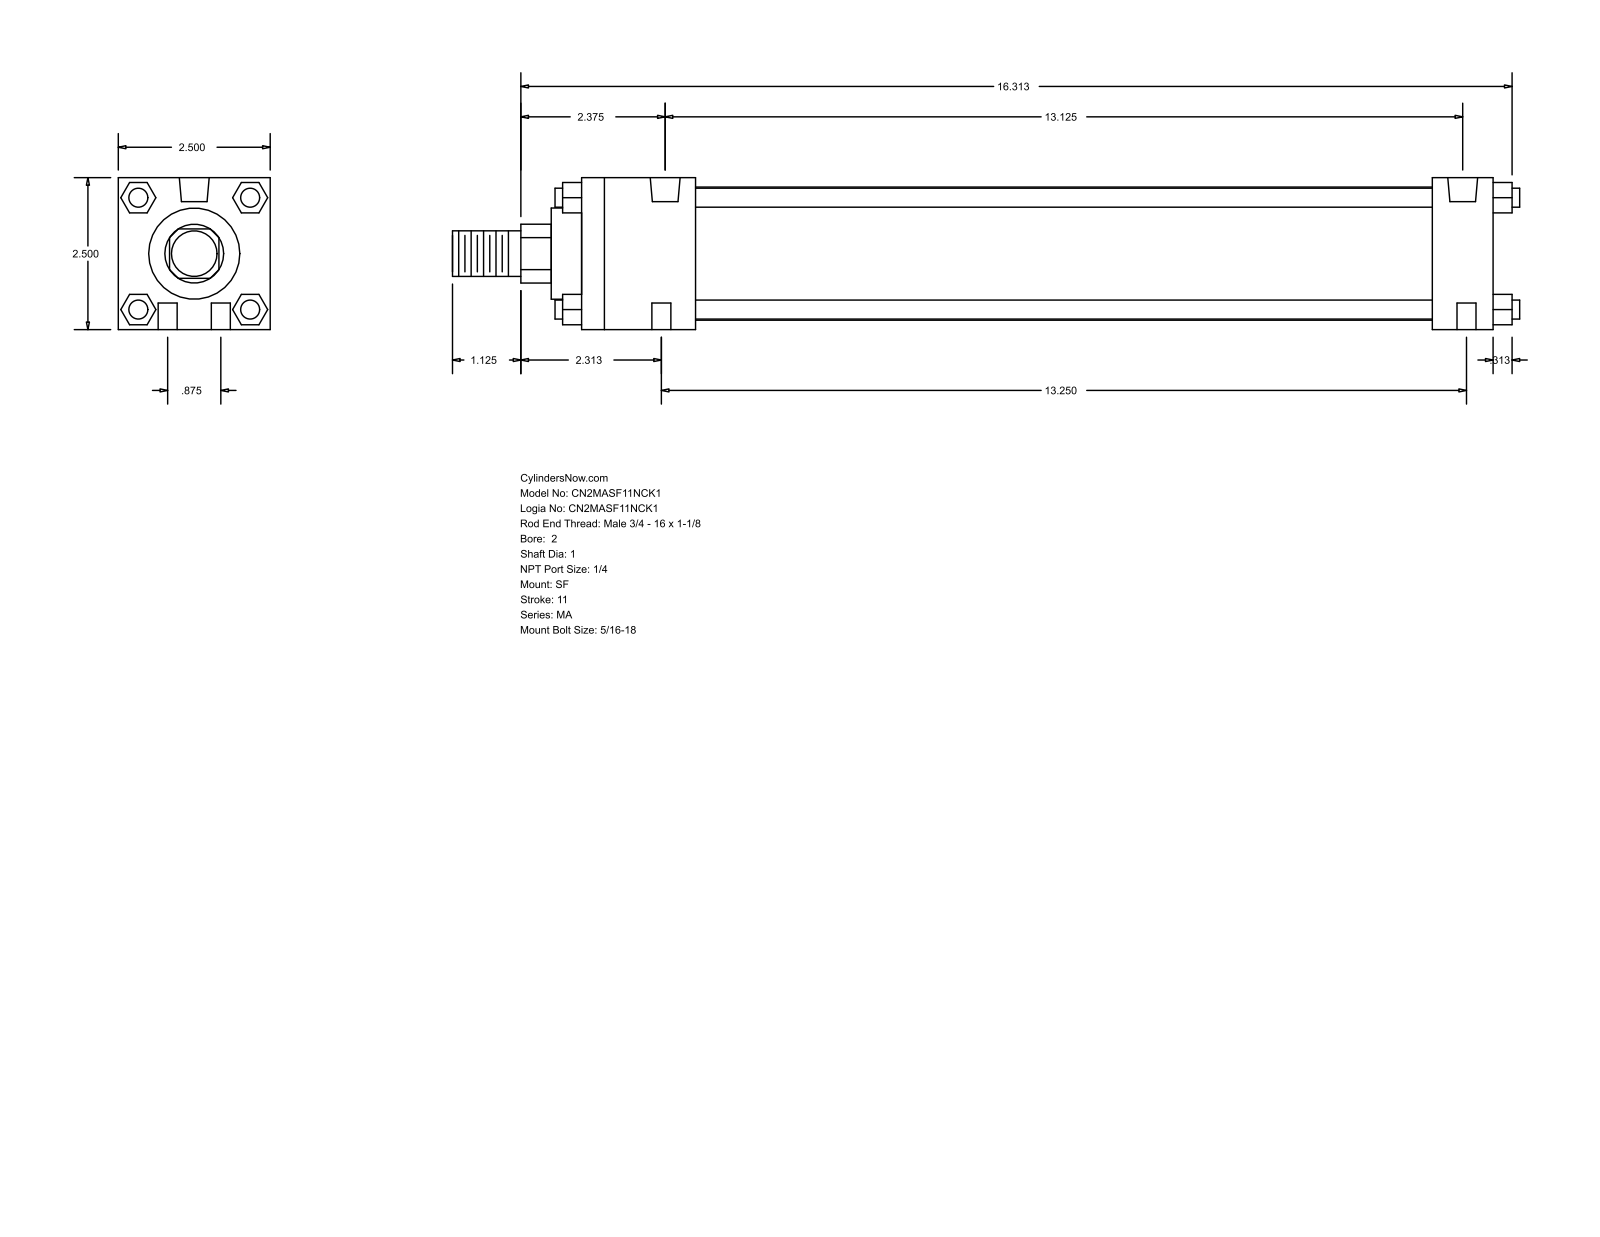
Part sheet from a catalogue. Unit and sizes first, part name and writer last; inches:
Units: inches
Overall size (bounding box): 17.563 × 2.5 × 2.5
Round holes (diameter × count): ⌀0.313 ×6, ⌀0.492 ×2
Round bosses / shafts (diameter × count): ⌀0.313 ×4, ⌀2.19 ×1, ⌀1.5 ×1, ⌀1 ×1, ⌀0.75 ×1
Partial cylindrical surfaces — rounded edges, fillets, slot ends (radius × count): R0.484 ×1
Main face-to-face distances: 2.5, 15, 0.5, 1, 14, 1.875, 12.125, 13.125, 0.92, 1.593
Hole centre spacings: 0.442, 13.194, 0.875, 13.125, 13.25, 13.279
Bodies: 0 solids, 124 faces (94 planar, 30 cylindrical, 0 other)
Part name (STEP PRODUCT): MA_SF__0200_1
STEP written by: GSSL Pune (CONFIG_CONTROL_DESIGN)
